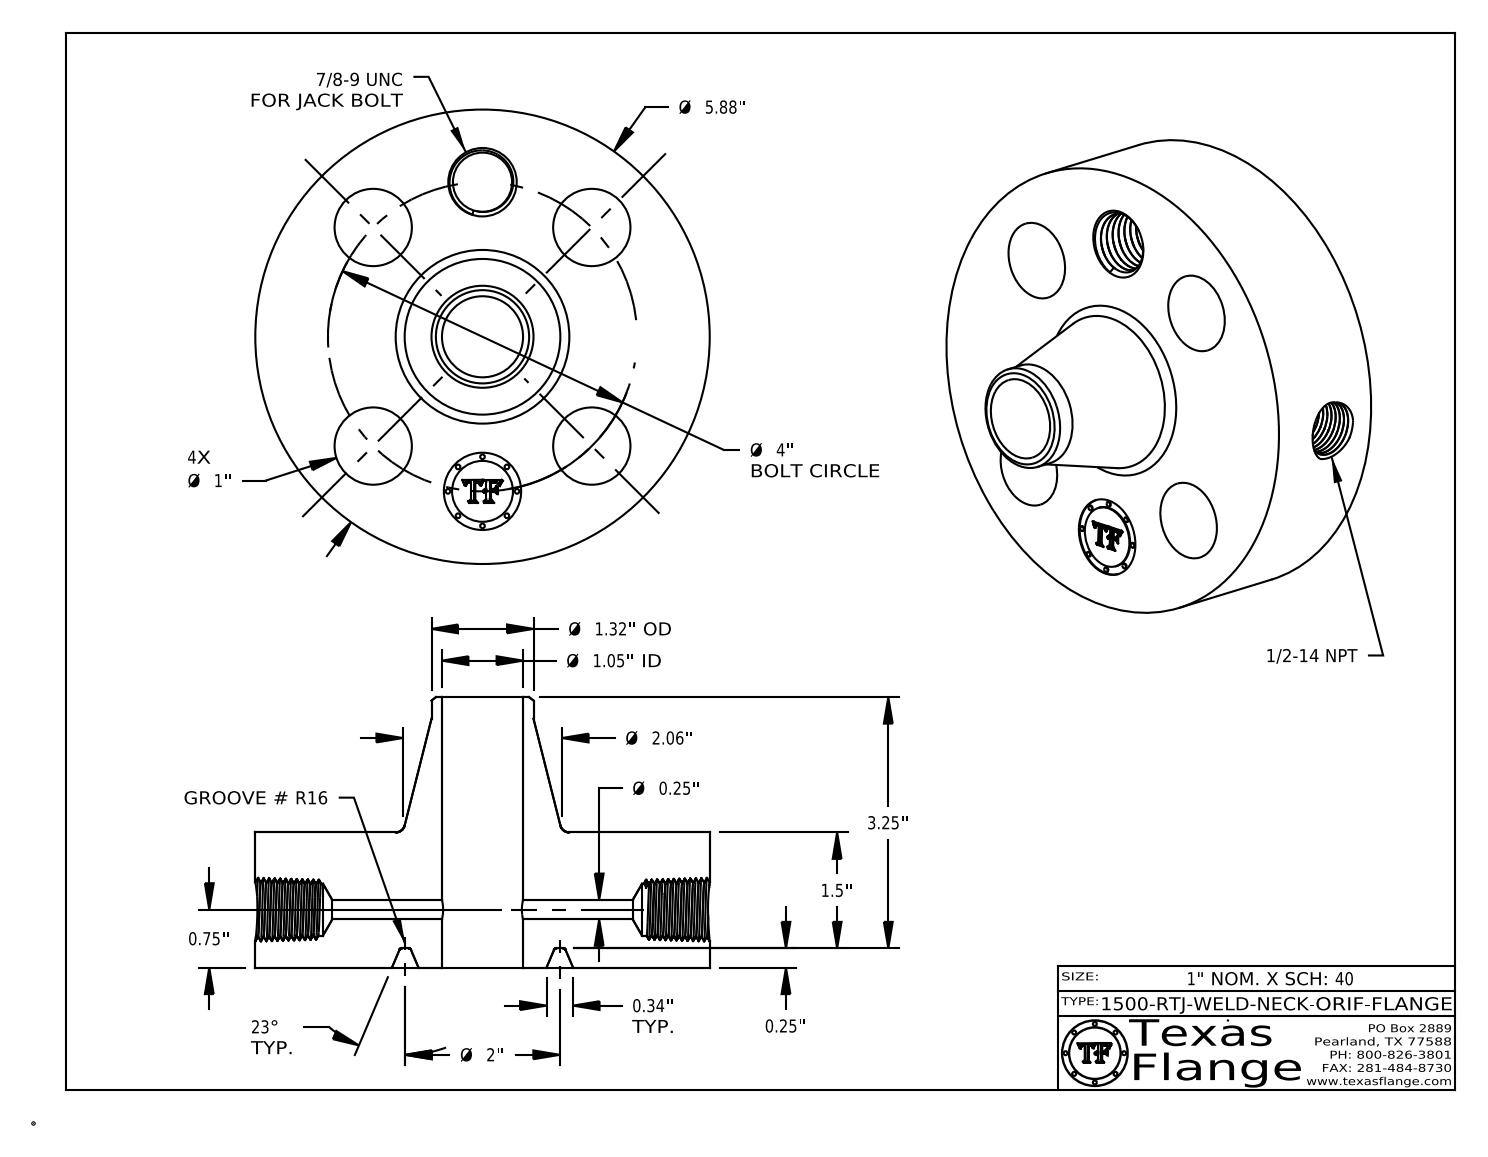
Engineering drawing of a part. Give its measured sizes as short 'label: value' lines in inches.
name: 1500-RTJ-WELD-NECK
written by: CATIA V5 STEP AP214 (AUTOMOTIVE_DESIGN)
unit: in
bodies: 1 solid, 771 faces (370 planar, 85 cylindrical, 316 other)
size: 5.88 × 5.88 × 3.5
volume: 40.51 in³; area: 135.6 in²
holes: 5× ⌀1, 1× ⌀0.25, 1× ⌀0.672, 1× ⌀0.766, 1× ⌀1.049
bosses: 8× ⌀0.061, 1× ⌀5.88, 1× ⌀1.32, 1× ⌀0.788
face distances: 1.75, 0.25, 1.5, 1.735, 1.485, 0.015, 3.5, 3.25, 1.765, 0.298
hole spacings: 2, 1.531, 2.828, 3.695, 4
